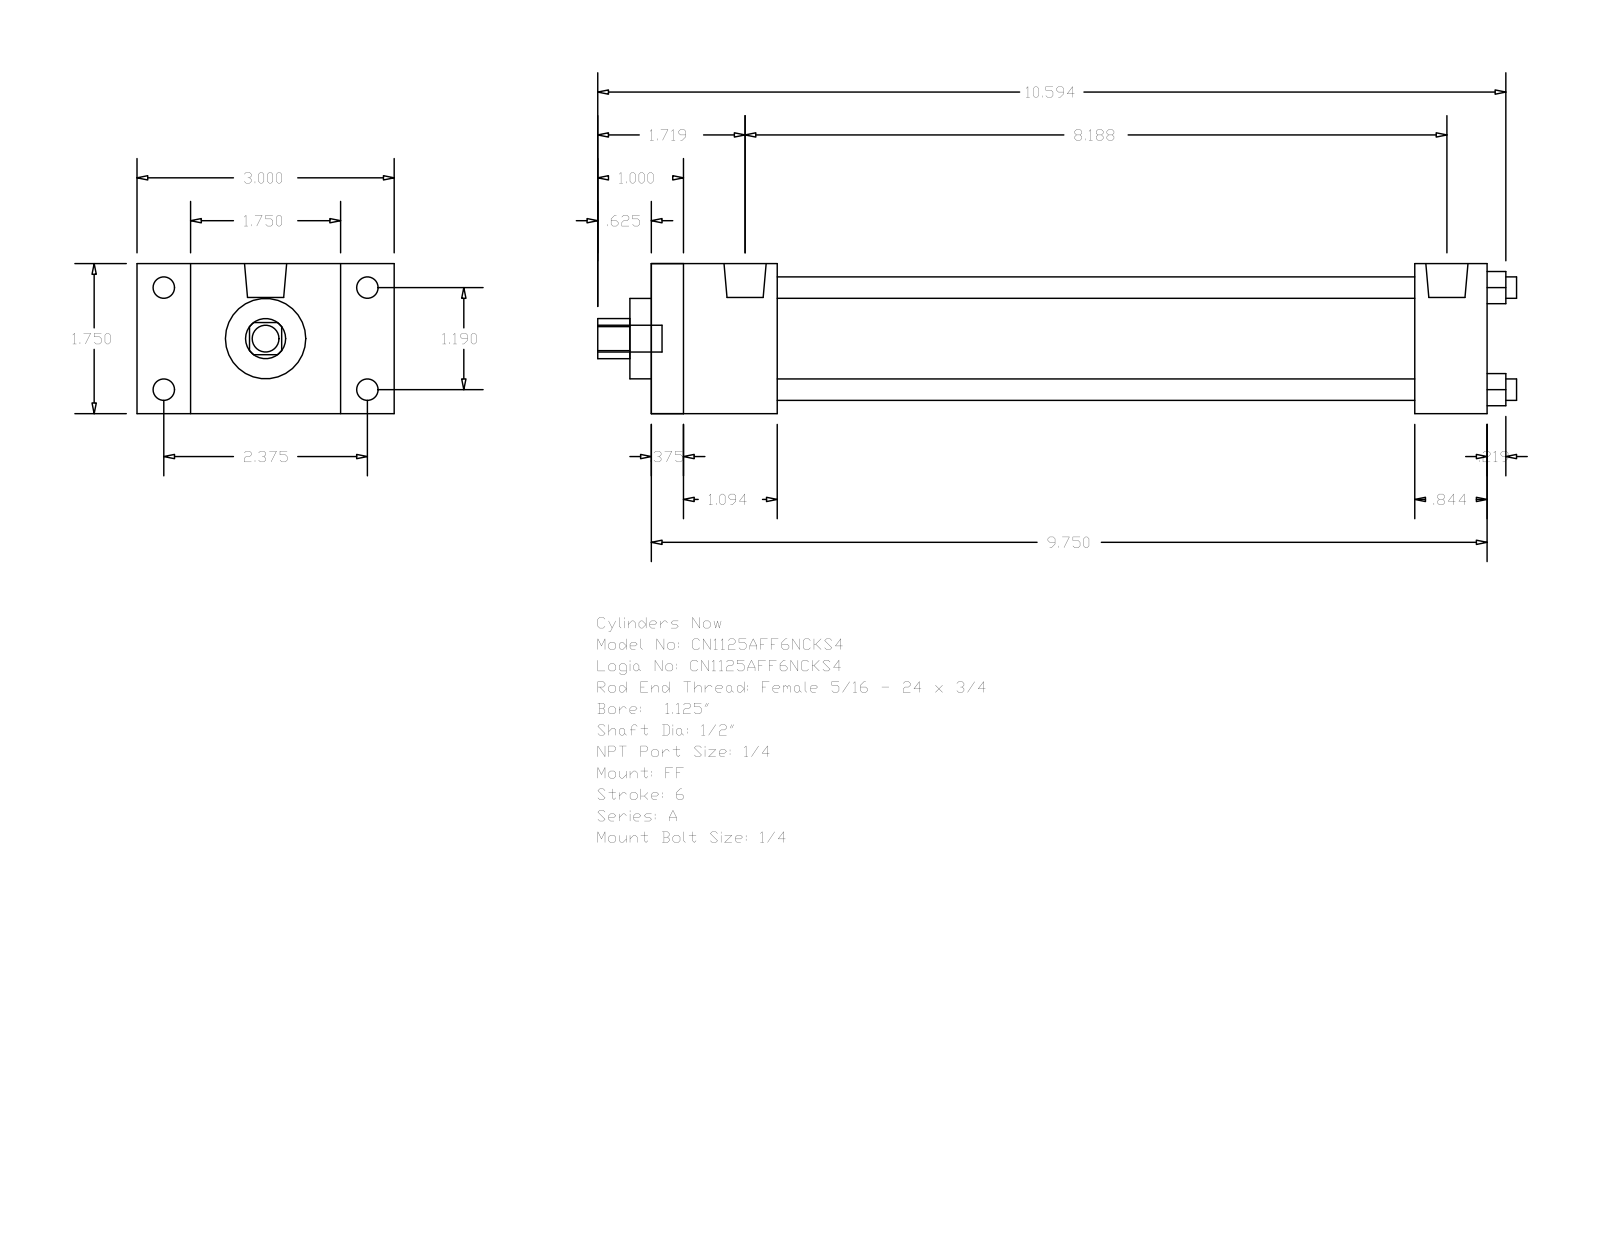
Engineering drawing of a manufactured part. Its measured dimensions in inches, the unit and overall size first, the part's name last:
Units: inches
Overall size (bounding box): 10.719 × 3 × 1.75
Round holes (diameter × count): ⌀0.25 ×4, ⌀0.5 ×1, ⌀0.937 ×1, ⌀1.255 ×1
Round bosses / shafts (diameter × count): ⌀0.25 ×4, ⌀0.219 ×4, ⌀0.492 ×2, ⌀0.313 ×1
Partial cylindrical surfaces — rounded edges, fillets, slot ends (radius × count): R0.234 ×1
Main face-to-face distances: 1.75, 9.75, 0.375, 9.375, 0.625, 8.906, 8.531, 0.844, 1.469, 1.094
Hole centre spacings: 0.841, 1.19, 1.683
Bodies: 0 solids, 92 faces (64 planar, 28 cylindrical, 0 other)
Part name (STEP PRODUCT): A_FF__0112_0.5
STEP written by: GSSL Pune (CONFIG_CONTROL_DESIGN)
